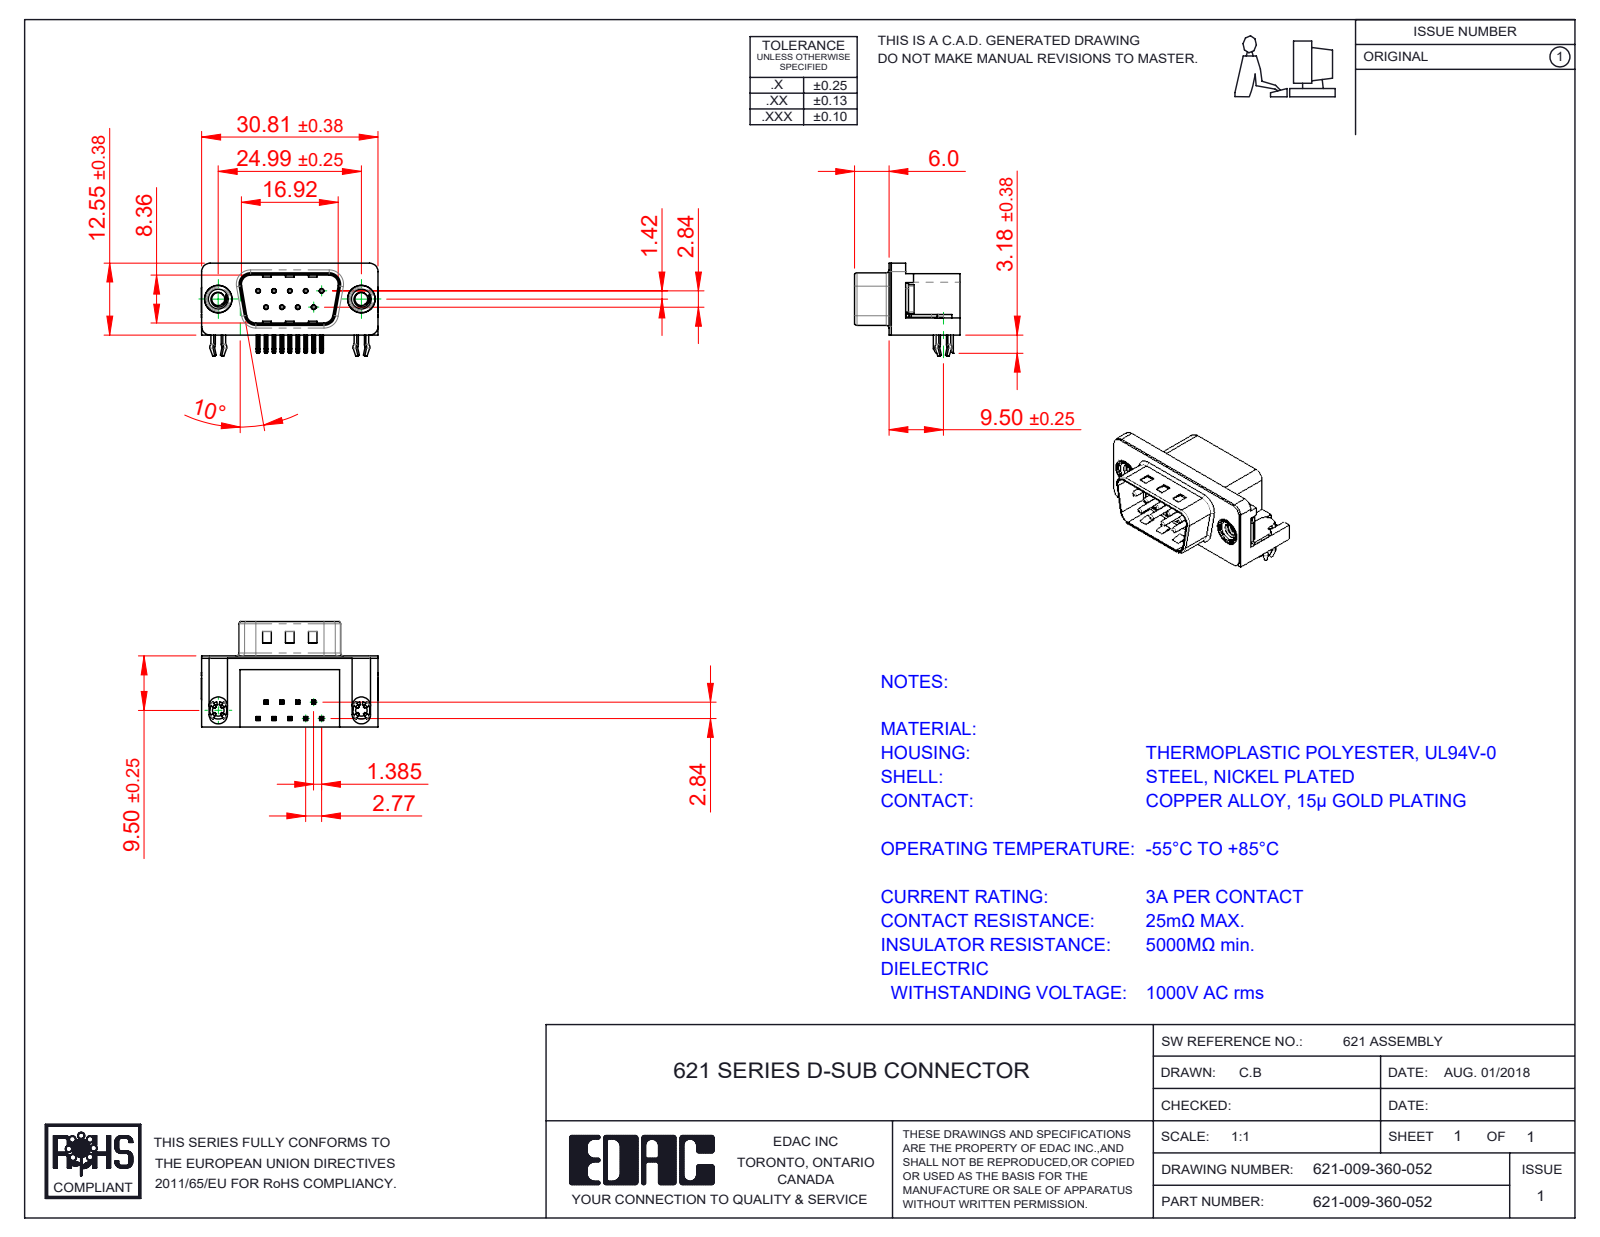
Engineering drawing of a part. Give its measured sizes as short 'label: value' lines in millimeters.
name: 621 Contact Top; 621-009-360-052; 621 Contact Bottom; 621 4-40 Threaded Board Mount (+3 more)
written by: SolidWorks 2016 (CONFIG_CONTROL_DESIGN)
unit: mm
bodies: 15 solids, 1021 faces (573 planar, 327 cylindrical, 121 other)
size: 30.89 × 18.4 × 15.73
volume: 3 259 mm³; area: 4 500 mm²
holes: 9× ⌀0.35, 9× ⌀0.8, 4× ⌀2.26, 2× ⌀4, 2× ⌀4.8, 2× ⌀5
bosses: 9× ⌀0.75, 2× ⌀4.9, 2× ⌀4.75, 2× ⌀3.9, 2× ⌀3.26
rounds: 44× R0.25, 18× R0.12, 16× R1, 9× R0.5, 8× R1.5, 8× R1.6, 4× R0.9, 4× R2
face distances: 0.4, 12, 12.4, 10.35, 2.9, 9.5, 2.5, 0.5, 2.1, 0.35
hole spacings: 3.16, 2.77, 5.54, 5.03, 5.04, 8.31, 7.48, 7.49
